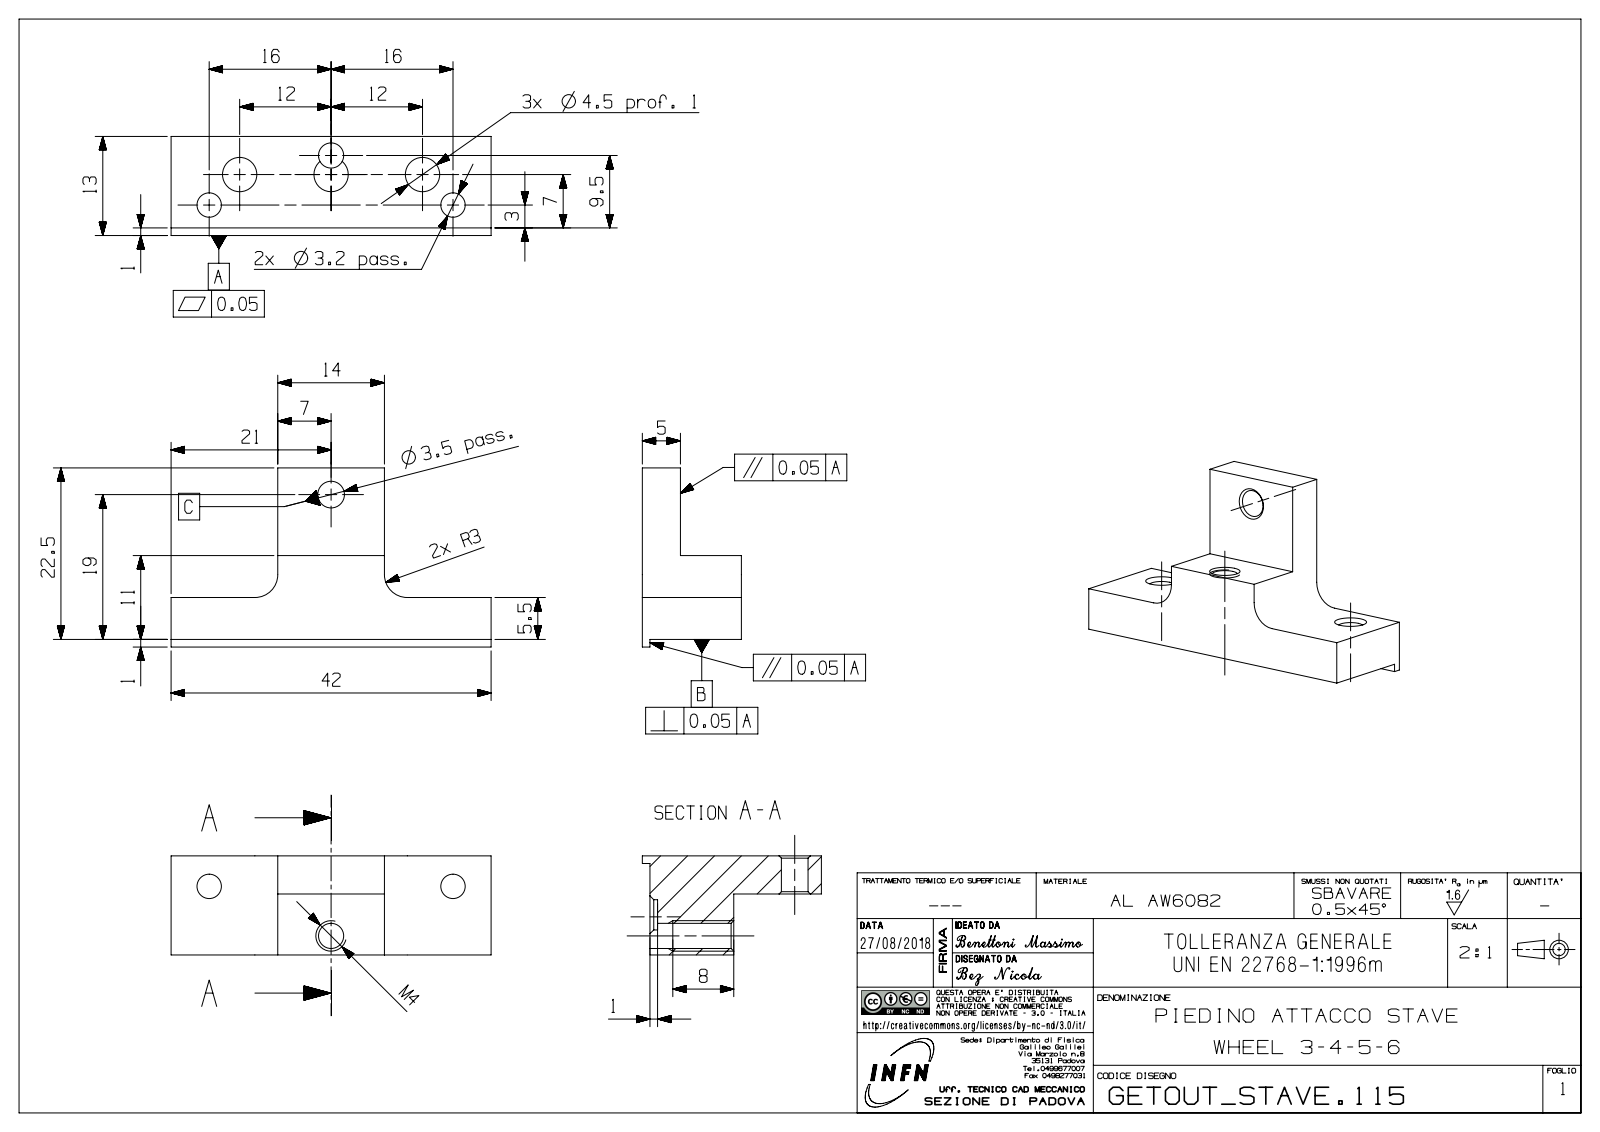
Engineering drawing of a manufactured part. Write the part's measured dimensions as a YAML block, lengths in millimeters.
part_name: "bez8324385A6v0q"
step_written_by: "SIEMENS PLM Software NX 12.0 (AUTOMOTIVE_DESIGN)"
units: millimeters
bodies: {solids: 1, faces: 36, planar: 17, cylindrical: 9, other: 10}
overall_size: [42, 23.5, 13]
volume: 4613
surface_area: 2711
round_holes:
  - {diameter: 3.2, count: 2}
  - {diameter: 4.5, count: 2}
  - {diameter: 3.3, count: 1}
  - {diameter: 3.5, count: 1}
partial_cylinders:
  - {radius: 3, count: 2}
  - {radius: 2.25, count: 1}
face_to_face_distances: [5.5, 13, 14, 5, 8, 28, 1, 11, 12, 42]
hole_center_spacings: [5.66, 12.26, 17.27, 28.28, 24, 32]
